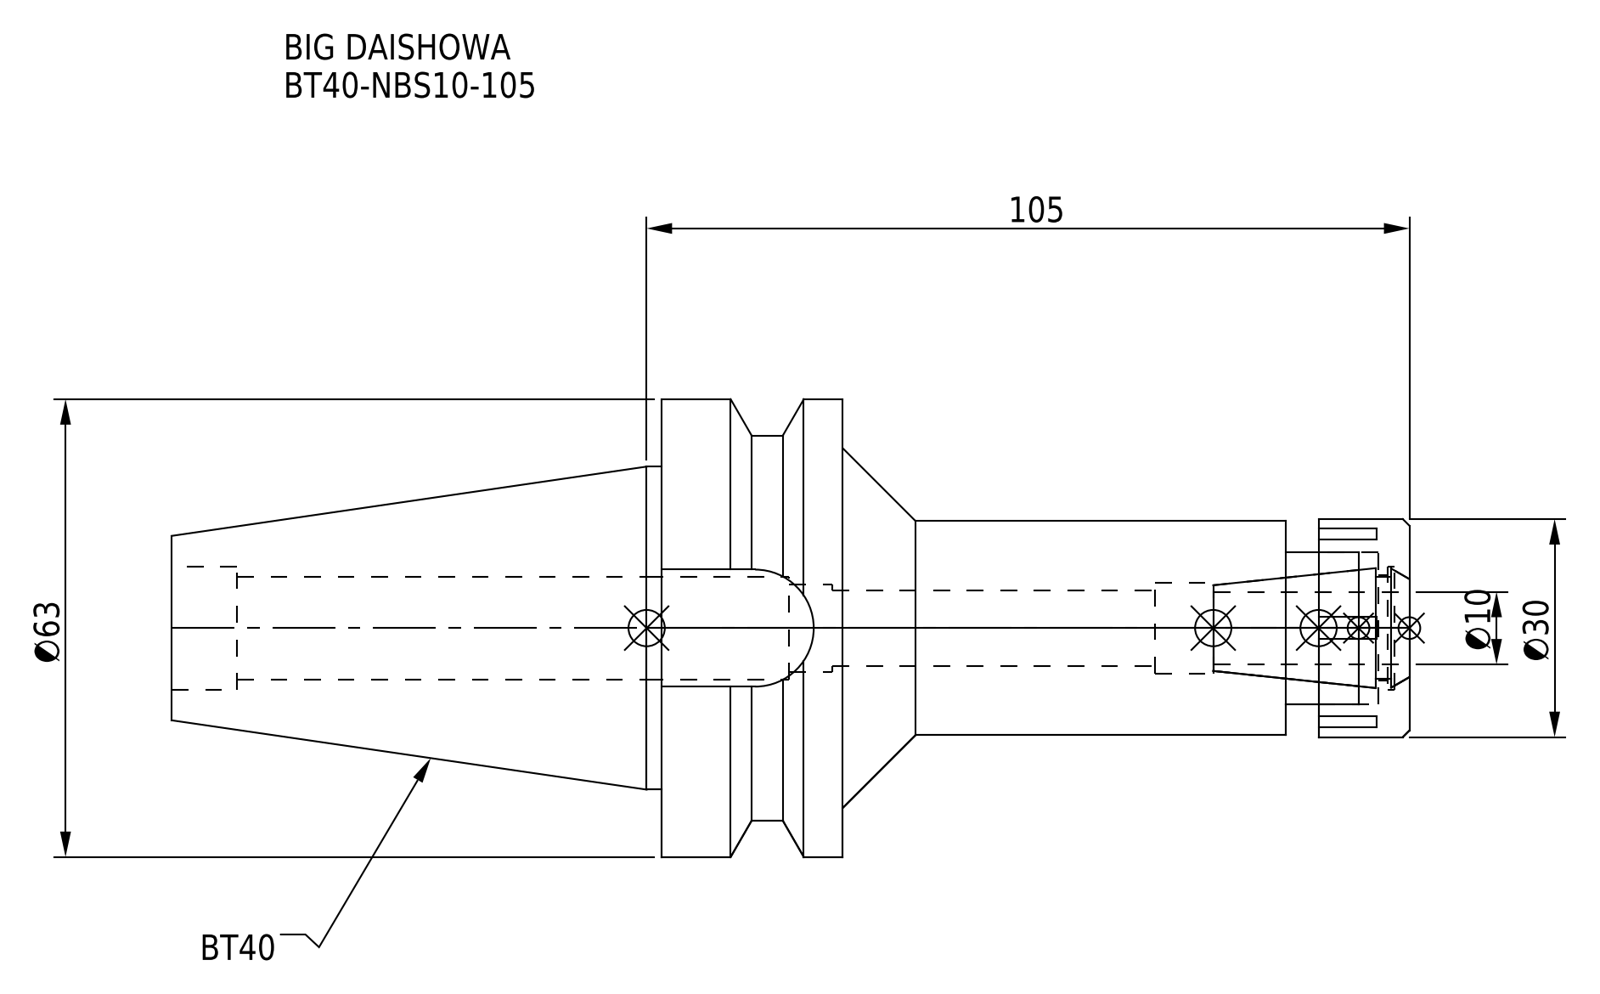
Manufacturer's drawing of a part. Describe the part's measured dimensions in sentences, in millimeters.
The part is named "BT40-NBS10-105_1.stp; BT40-NBS10-105.stp; DXF_TEMP_ASSY_ASM_4_ASM.stp; BT40-NBS10-105 (+3 more)". Its 3-D file was written by "SolidWorks 2019 (CONFIG_CONTROL_DESIGN)". It is 2 solids with 93 faces: 45 planar, 34 cylindrical and 14 other. Overall it measures 170.4 by 63 by 63 millimeters. Its volume is 167 456 cubic millimeters and its surface area 34 398 square millimeters. Round holes: 1 of diameter 10.4, 1 of diameter 12, 1 of diameter 12.5, 1 of diameter 14.2, 1 of diameter 14.5, 1 of diameter 17, 1 of diameter 21. Round bosses or shafts: 1 of diameter 63, 1 of diameter 53, 1 of diameter 44.45, 1 of diameter 30, 1 of diameter 29.5. Partial cylindrical surfaces (rounded edges, fillets, slot ends): 1 of radius 8.05. The main face-to-face distances are 25, 78, 103, 4.5, 12.5, 17, 61, 86, 65.5, 90.5.
